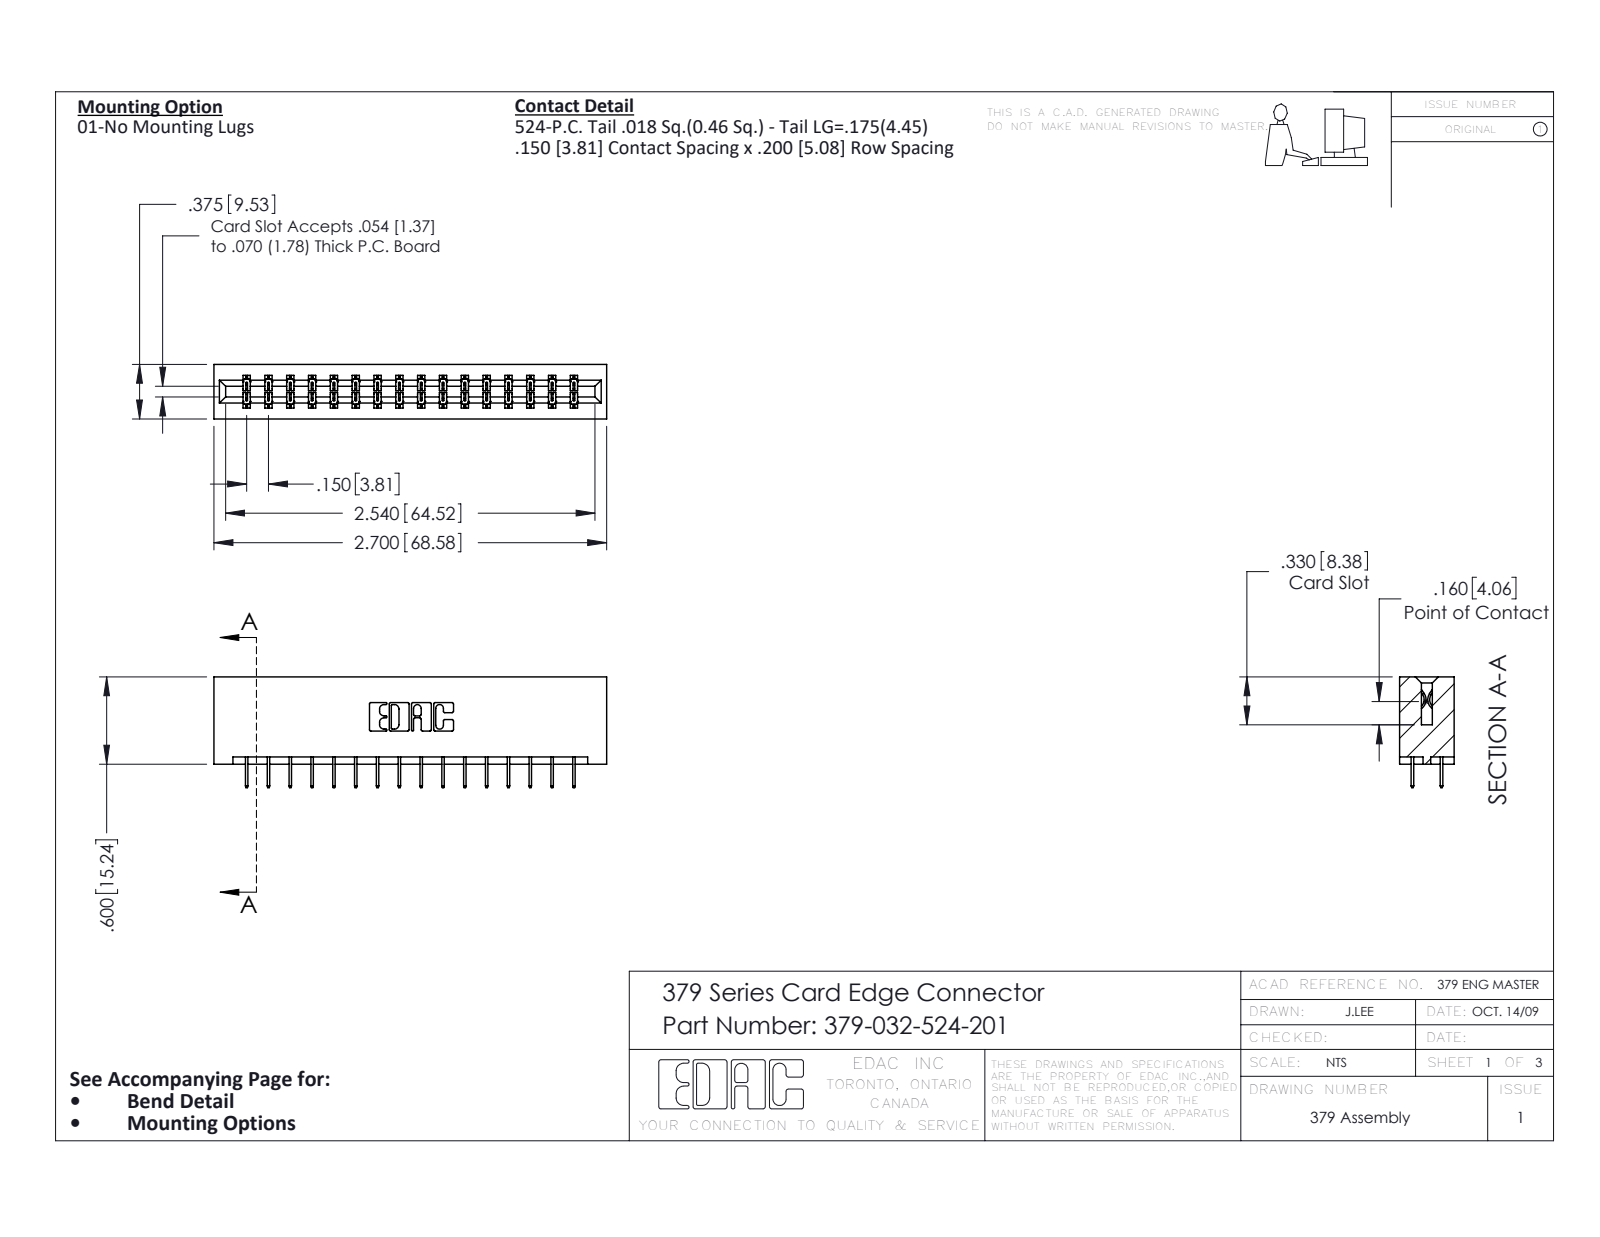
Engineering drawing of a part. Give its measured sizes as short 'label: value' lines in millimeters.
name: 379-032-524-201; 379 Part_Lugless; 345-292-001_345-293-124
written by: SolidWorks 2020 (CONFIG_CONTROL_DESIGN)
unit: mm
bodies: 33 solids, 1898 faces (1410 planar, 488 cylindrical, 0 other)
size: 68.6 × 19.4 × 9.5
volume: 7 670 mm³; area: 8 271 mm²
rounds: 48× R0.2, 22× R0.3, 6× R0.2, 6× R0.8, 3× R0.7, 2× R0.4, 2× R0.6, 2× R0.6
face distances: 7.6, 1.9, 9.5, 5.1, 3.8, 2.5, 14, 15.2, 5.7, 1.3
